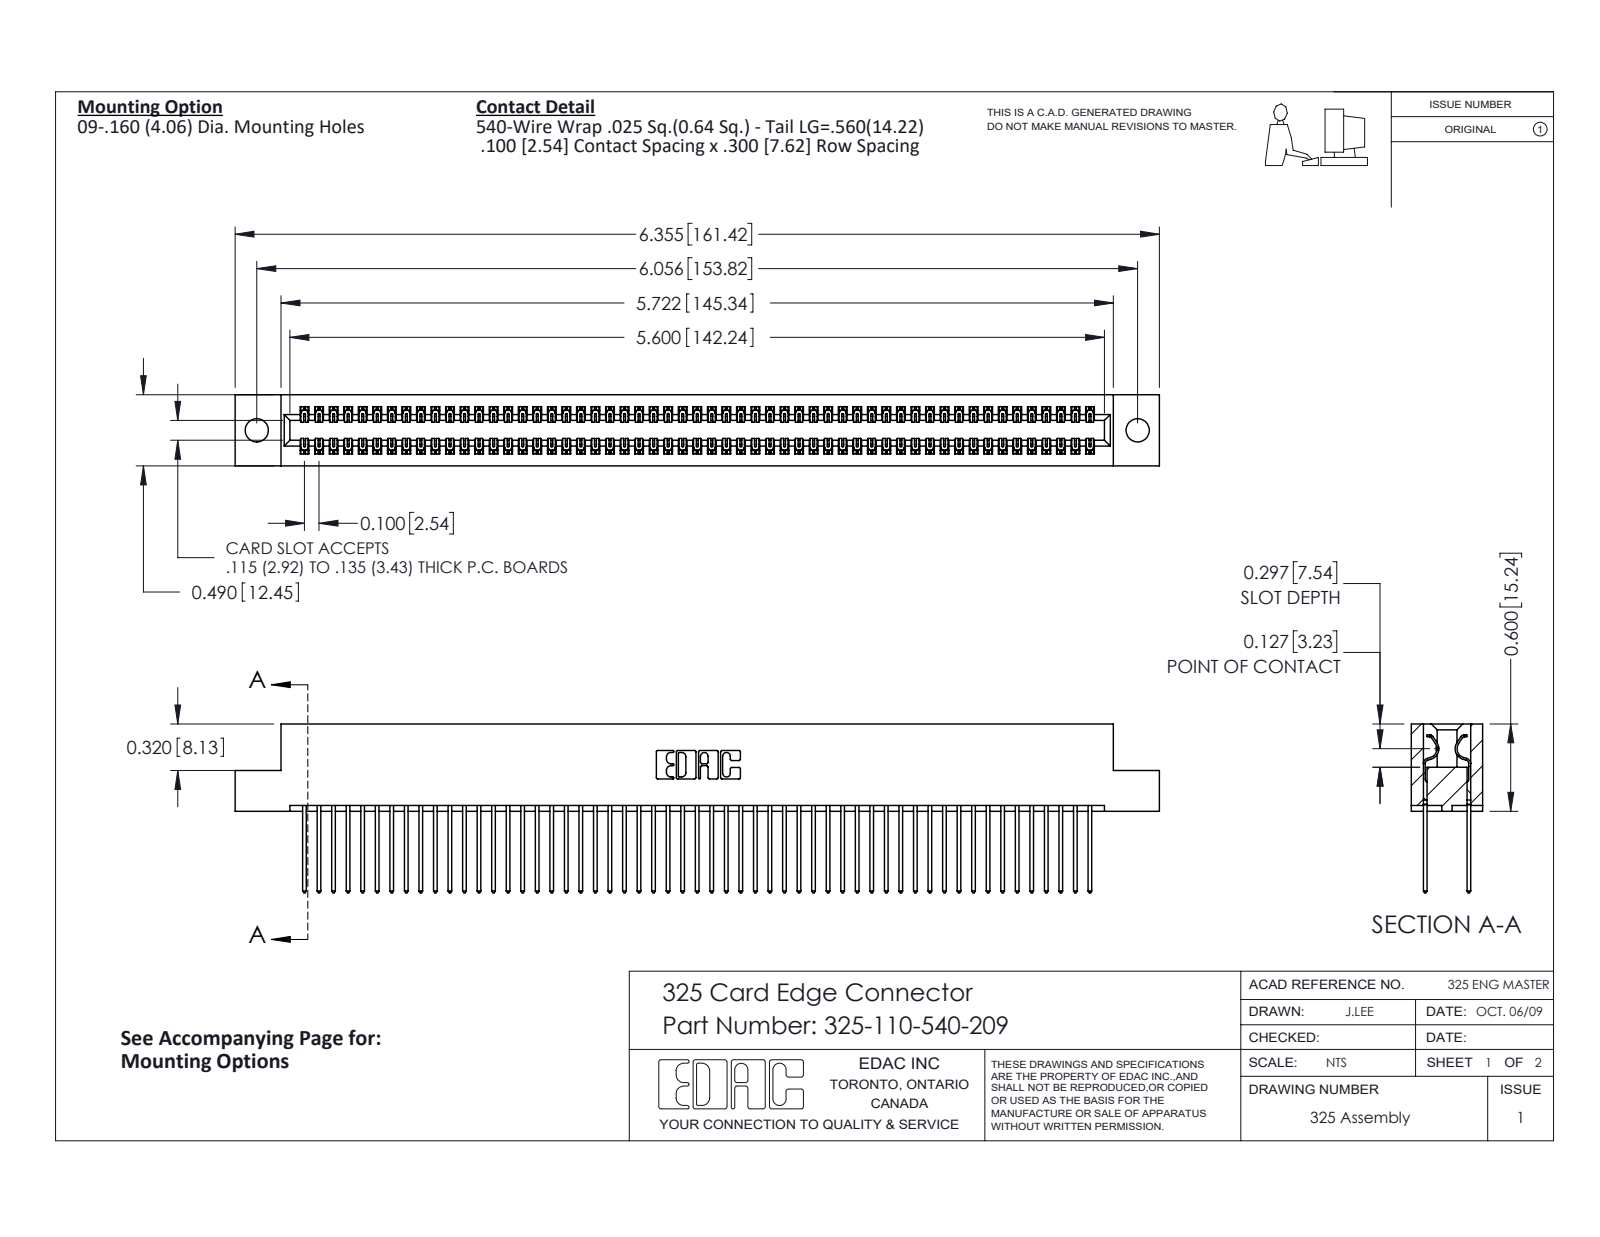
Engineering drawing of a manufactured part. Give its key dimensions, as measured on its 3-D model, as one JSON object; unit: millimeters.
{"part_name": "325 Part_.160 TH; 325-292-001_325-293-140; 325-110-540-209", "step_written_by": "SolidWorks 2016 (CONFIG_CONTROL_DESIGN)", "units": "millimeters", "bodies": {"solids": 111, "faces": 5834, "planar": 4030, "cylindrical": 1804, "other": 0}, "overall_size": [161.4, 29.5, 12.4], "volume_mm3": 21140, "surface_area_mm2": 27800, "round_holes": [[4.1, 2]], "partial_cylinders_radius": [[0.2, 165], [0.3, 110], [0.3, 22], [0.2, 6], [0.8, 6], [0.7, 3], [0.4, 2], [0.6, 2]], "face_to_face_distances": [2.1, 10.3, 7.6, 2.7, 9.7, 0.6, 8.3, 12.4, 7, 14.2], "hole_center_spacings": [153.8]}
